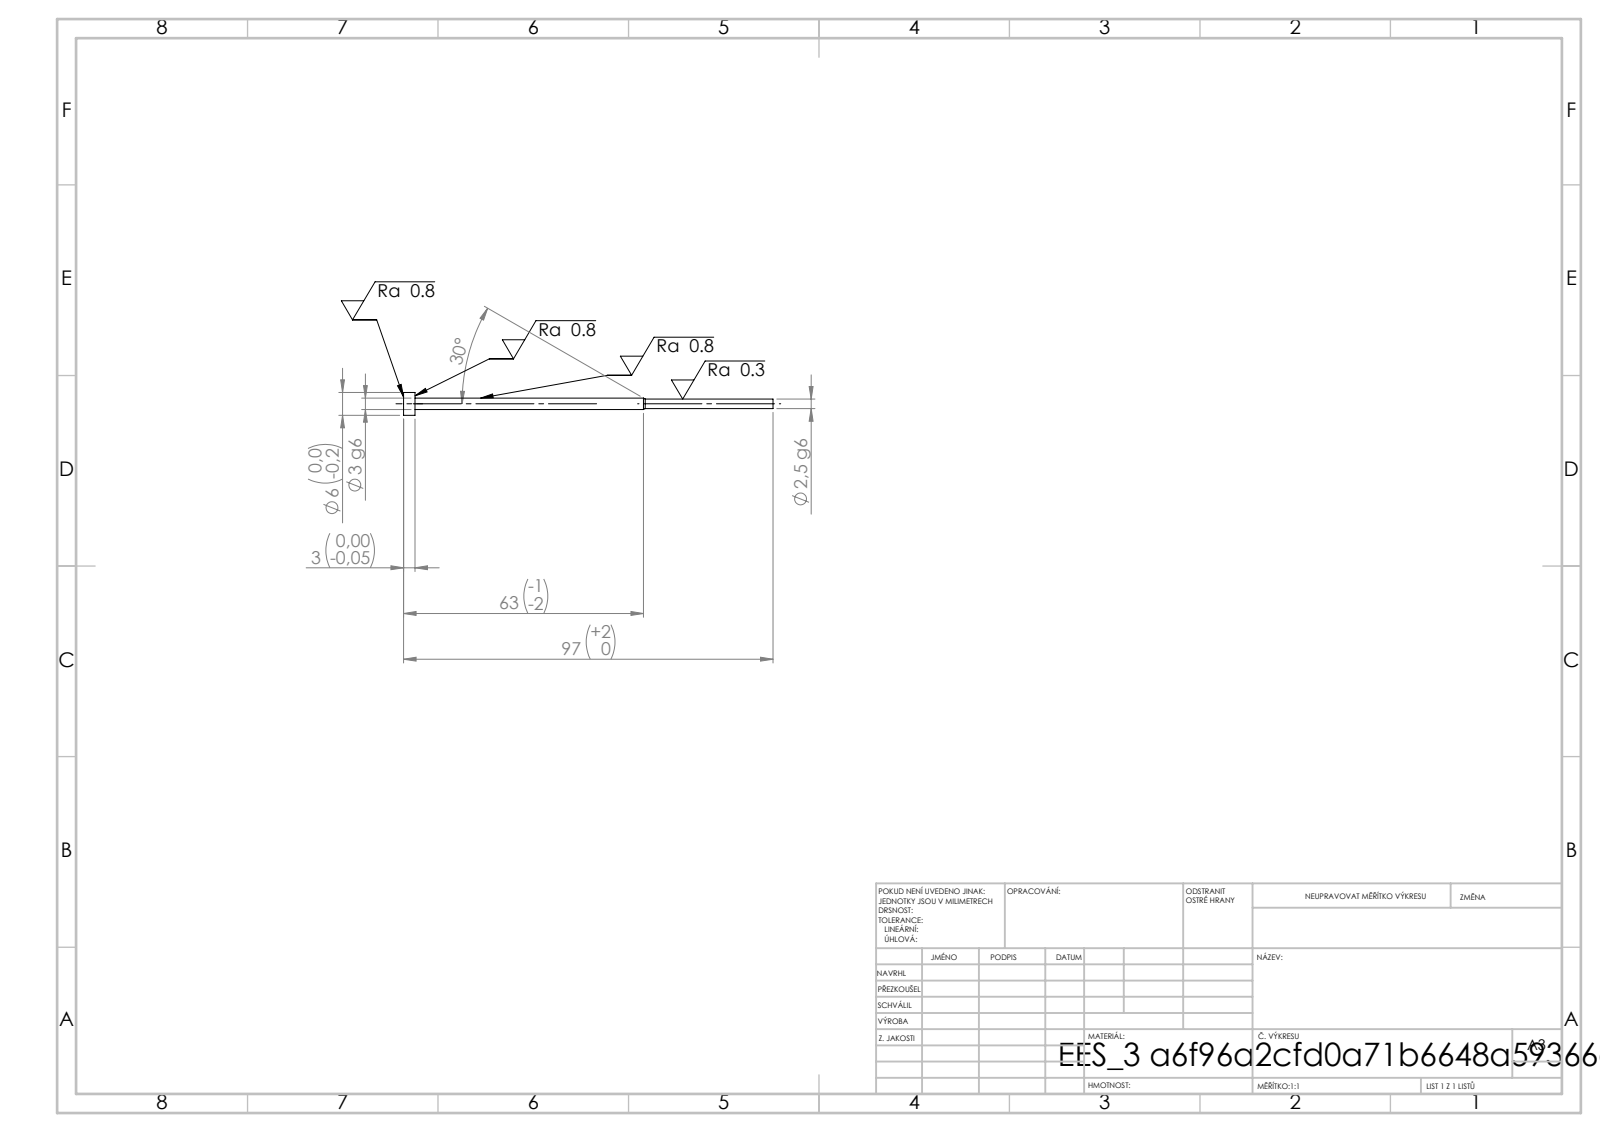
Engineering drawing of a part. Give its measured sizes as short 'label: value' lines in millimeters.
written by: SolidWorks 2019 (CONFIG_CONTROL_DESIGN)
unit: mm
bodies: 1 solid, 11 faces (3 planar, 6 cylindrical, 2 other)
size: 97 × 6 × 6
volume: 676 mm³; area: 944 mm²
bosses: 1× ⌀6, 1× ⌀3, 1× ⌀2.5
face distances: 3, 94, 97
